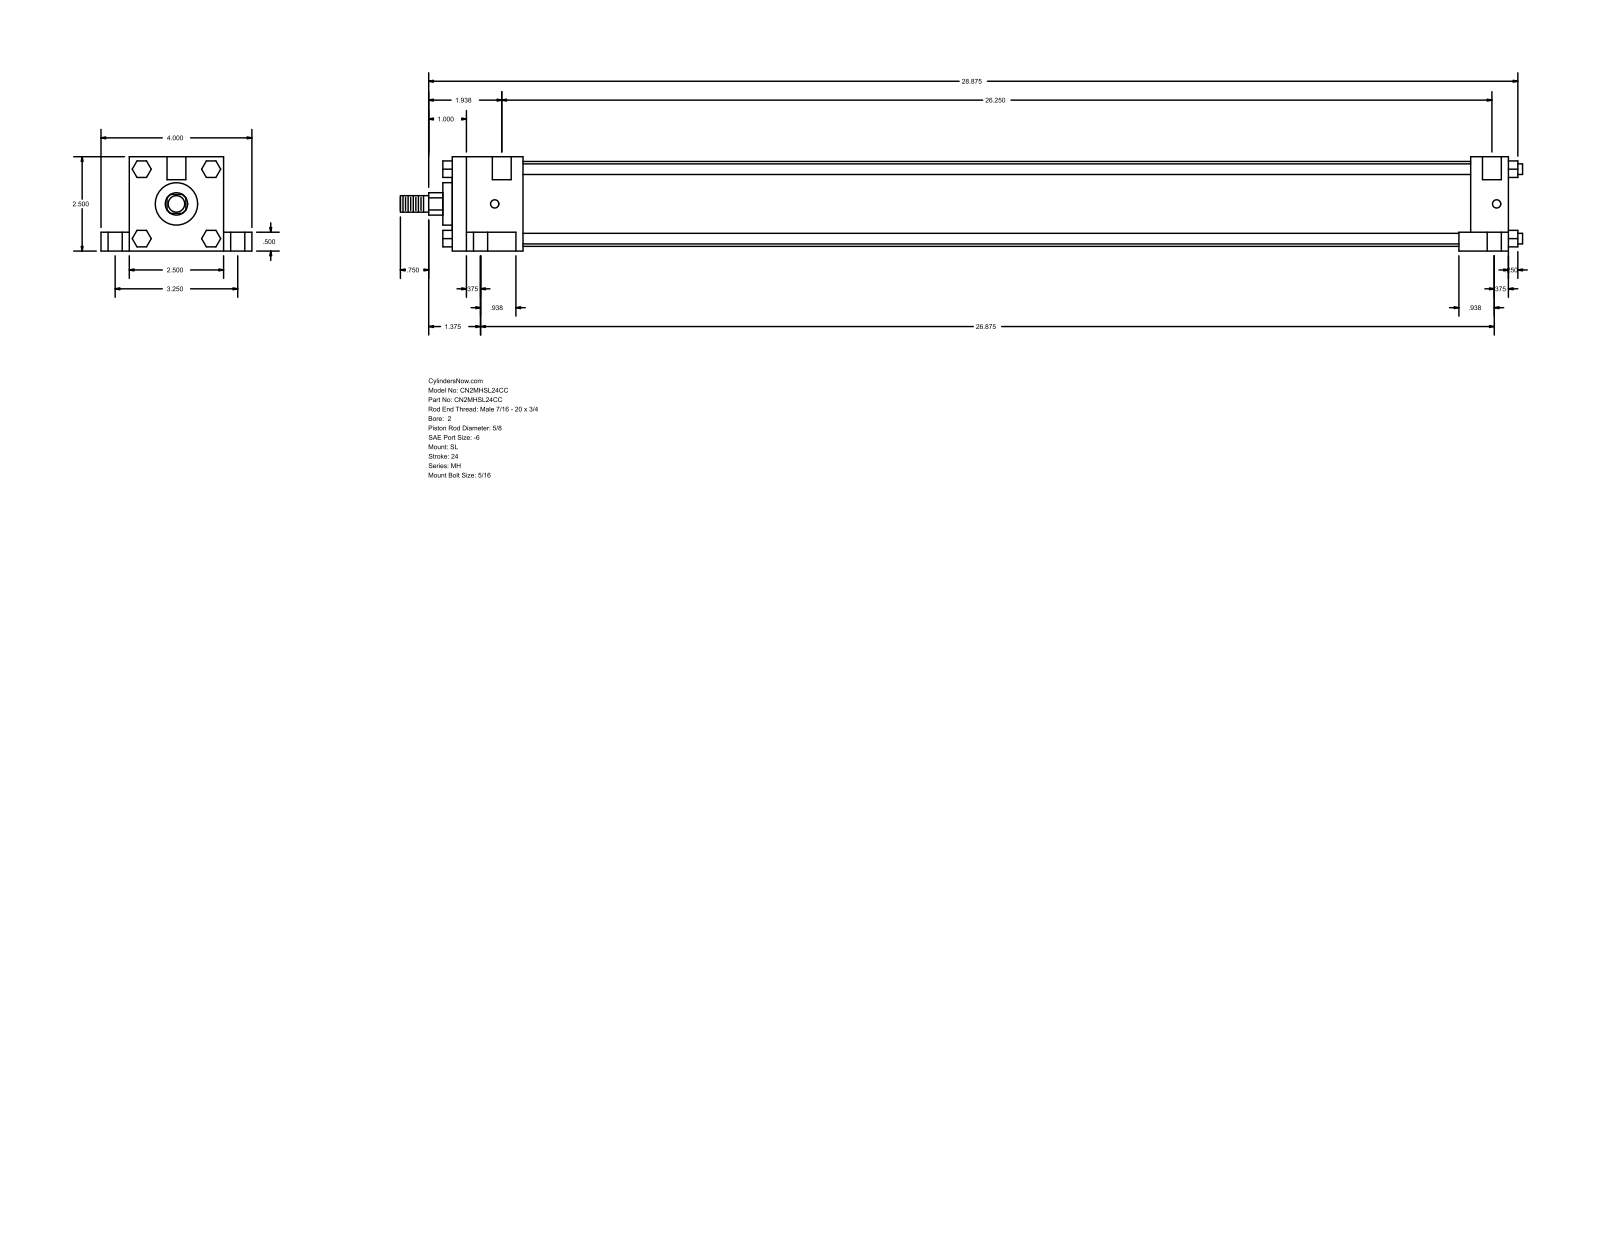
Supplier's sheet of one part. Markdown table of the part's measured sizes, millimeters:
| quantity | value |
| --- | --- |
| part name | MH_SL__0200_0.625 |
| STEP written by | GSSL Pune (CONFIG_CONTROL_DESIGN) |
| units | millimeters |
| bodies | 0 solids, 148 faces (112 planar, 36 cylindrical, 0 other) |
| overall size | 755.65 × 101.6 × 63.5 |
| round holes (diameter × count) | 5.56 × 4, 9.53 × 4, 15.88 × 4, 12.7 × 2 |
| round bosses / shafts (diameter × count) | 7.14 × 4, 57.15 × 1, 28.57 × 1, 15.88 × 1, 11.11 × 1 |
| partial cylindrical surfaces (radius × count) | 7.54 × 1 |
| main face-to-face distances | 63.5, 711.2, 12.7, 19.05, 82.55, 50.8, 685.79, 25.41, 47.62, 638.17 |
| hole center spacings | 41.3, 42.36, 43.67, 82.54, 669.61, 674.36, 674.69, 682.29 |
